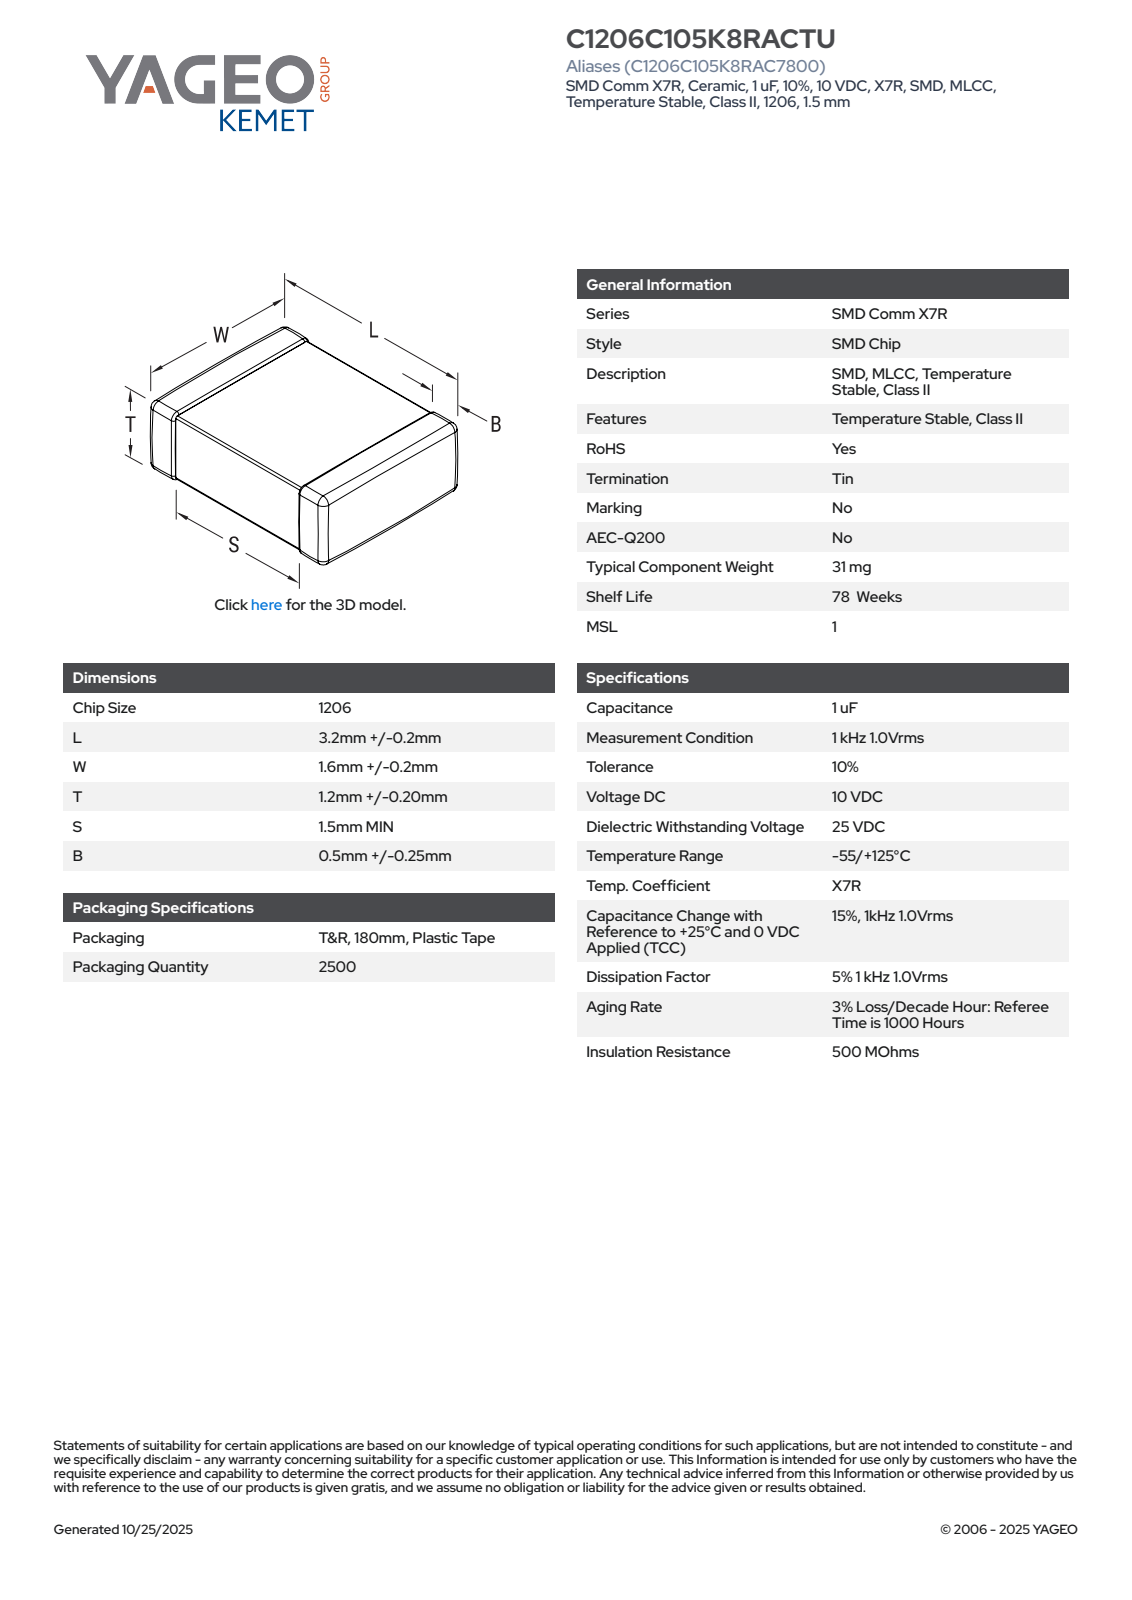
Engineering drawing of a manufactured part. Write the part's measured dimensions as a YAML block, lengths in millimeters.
part_name: "CCS_CCSTDNOS_1206_L3.4W1.8T1.4B0.75"
step_written_by: "SolidWorks 2014 (AUTOMOTIVE_DESIGN)"
units: millimeters
bodies: {solids: 4, faces: 125, planar: 71, cylindrical: 38, other: 16}
overall_size: [3.4, 1.8, 1.4]
volume: 8
surface_area: 26
face_to_face_distances: [1.36, 1.76, 1.32, 1.72, 1.4, 3.4, 1.8, 1.37, 1.33, 0.99]
